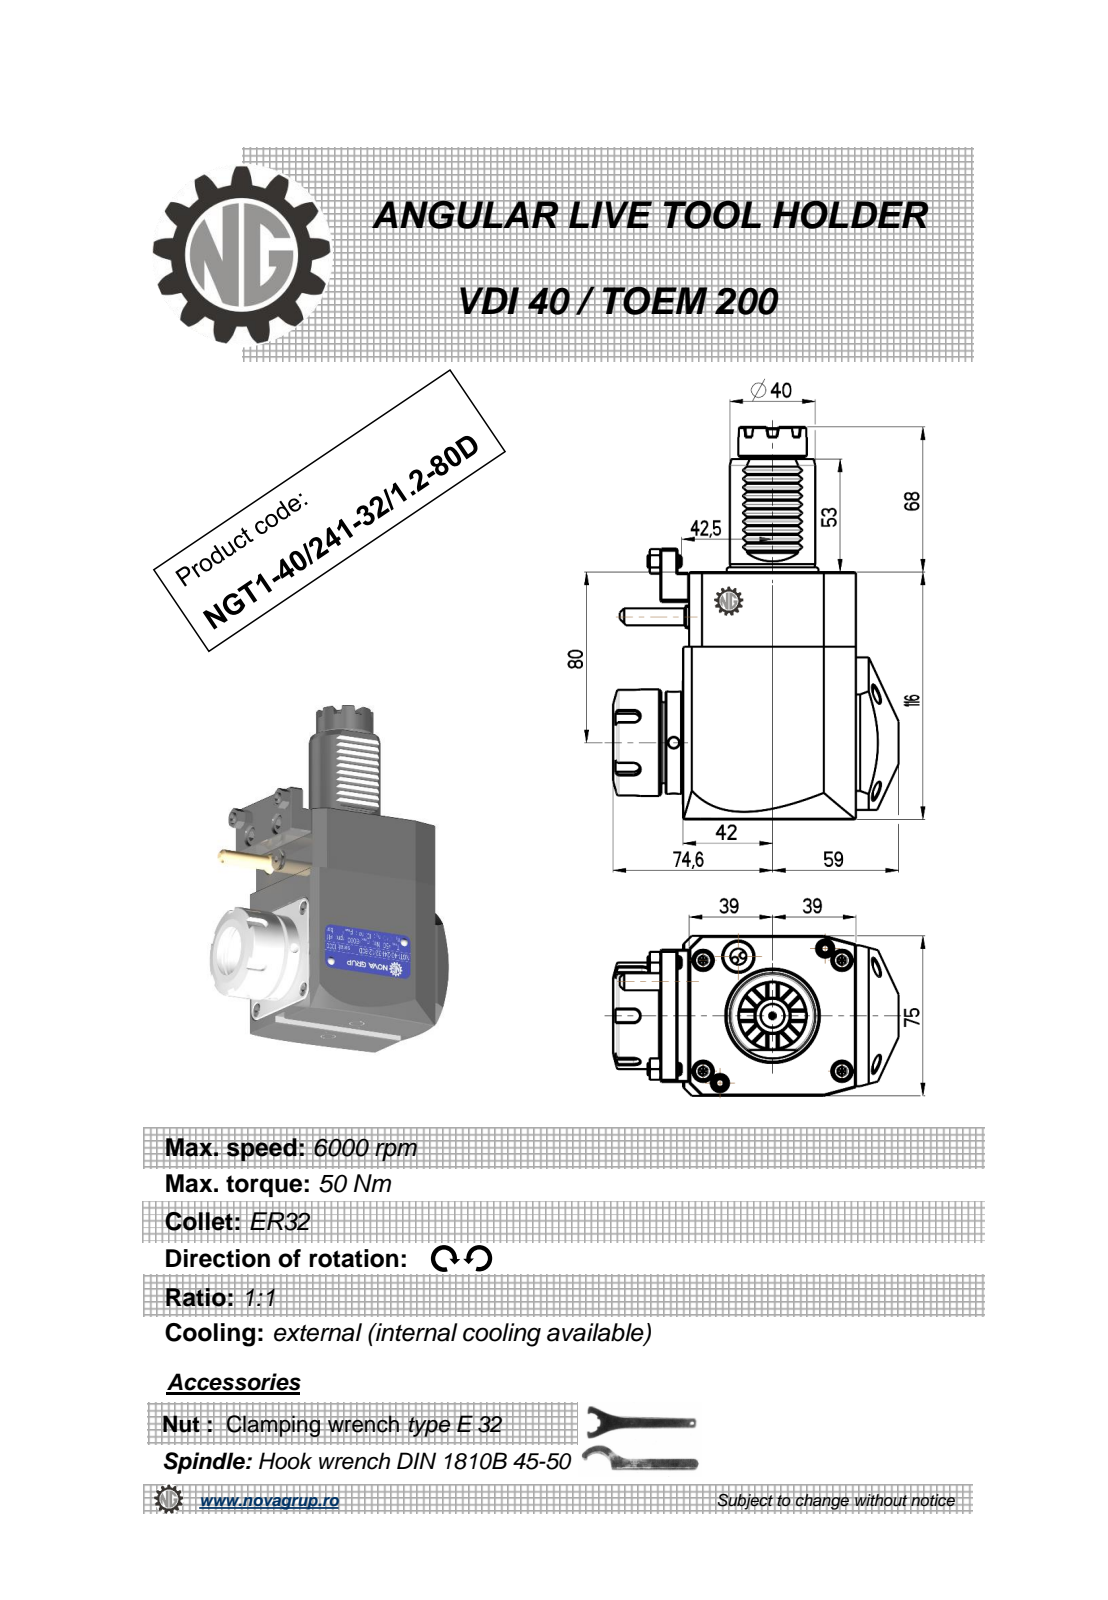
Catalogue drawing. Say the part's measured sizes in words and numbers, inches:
The part is named "NGT1_40_241_32_1_2_80D". Its 3-D file was written by "PRO/ENGINEER BY PARAMETRIC TECHNOLOGY CORPORATION, 2010280 (CONFIG_CONTROL_DESIGN)". It is 1 solid with 473 faces: 207 planar, 89 cylindrical and 177 other. Overall it measures 7.244 by 5.26 by 3.016 inches. Its volume is 54.05 cubic inches and its surface area 111.4 square inches. Round holes: 3 of diameter 0.197, 1 of diameter 0.118, 1 of diameter 1.063. Round bosses or shafts: 2 of diameter 0.236, 1 of diameter 1.969, 1 of diameter 1.89, 1 of diameter 1.614, 1 of diameter 1.575, 1 of diameter 1.26, 1 of diameter 0.669, 1 of diameter 0.441. Partial cylindrical surfaces (rounded edges, fillets, slot ends): 10 of radius 0.012, 10 of radius 0.012, 6 of radius 0.009, 5 of radius 0.118, 1 of radius 0.02, 1 of radius 0.339, 1 of radius 1.575. The main face-to-face distances are 2.953, 4.567, 3.189, 0.531, 3.181, 0.413, 0.02, 0.421, 3.602, 0.118. The hole center spacings are 2.407.
